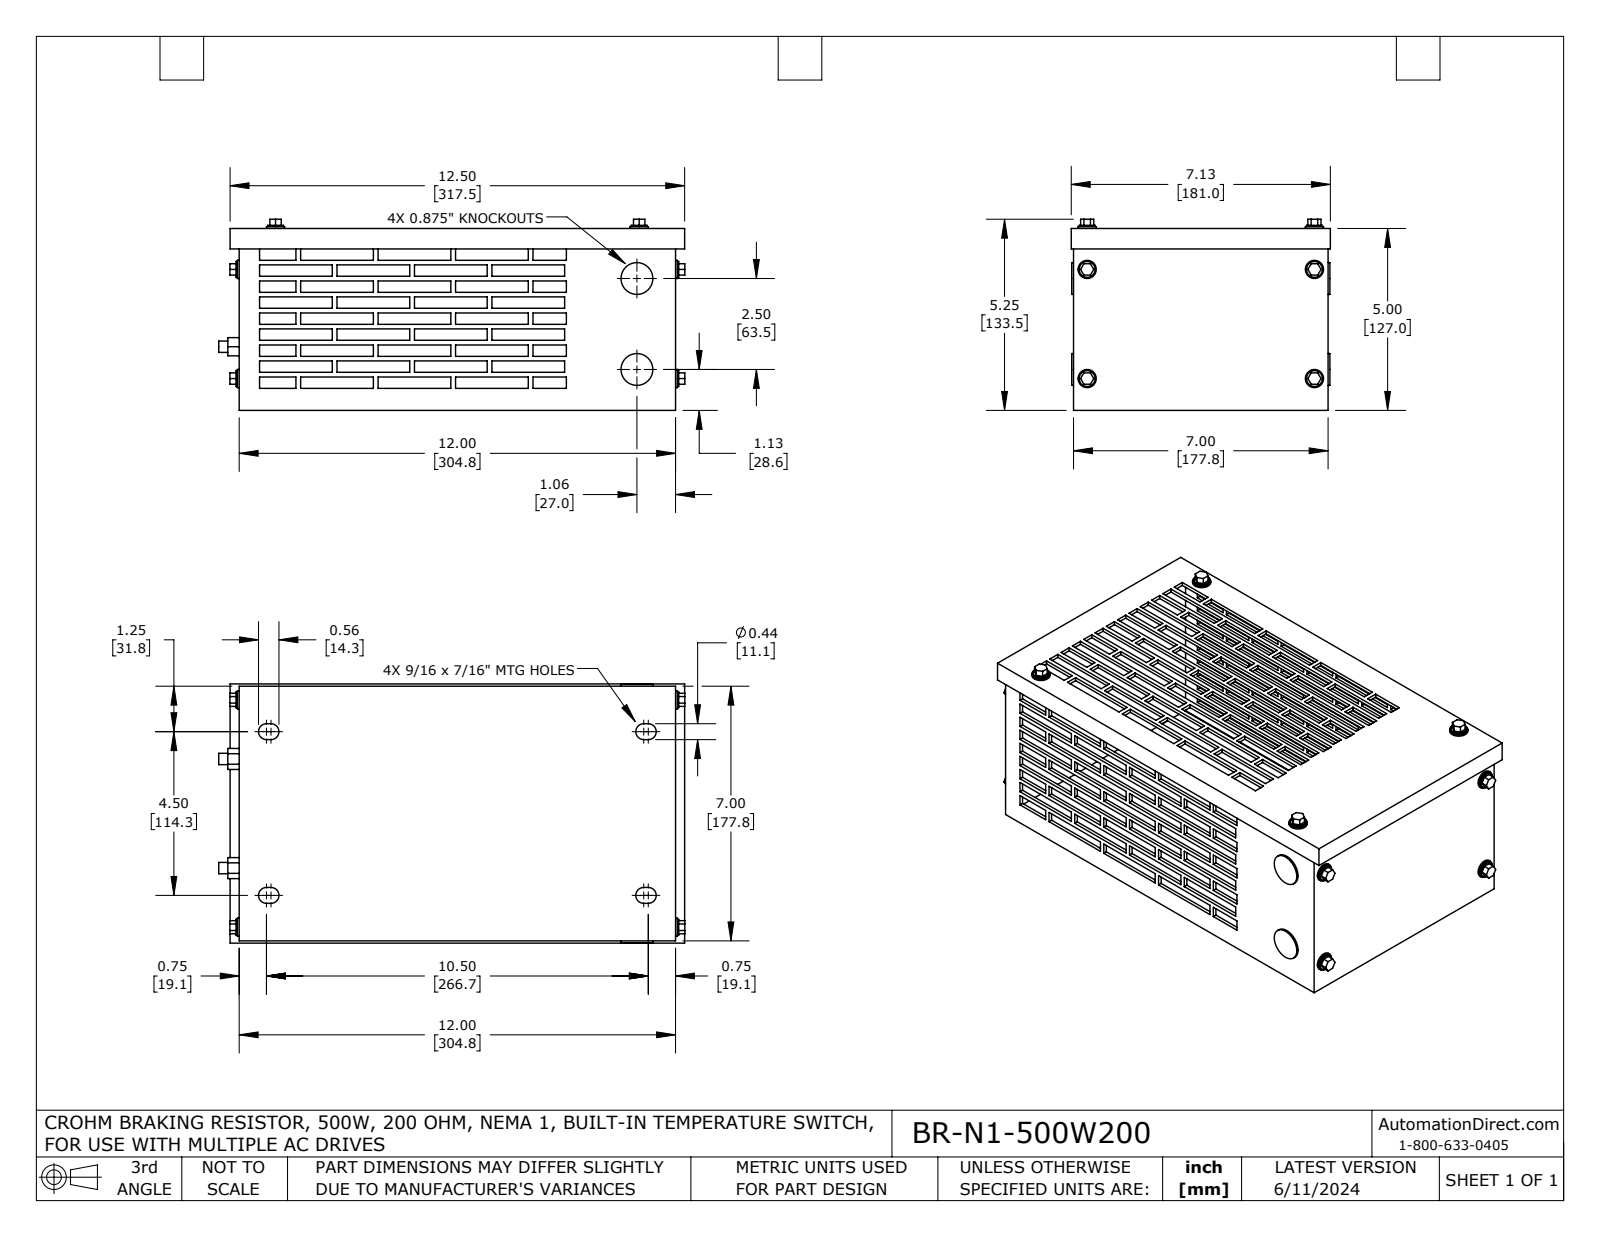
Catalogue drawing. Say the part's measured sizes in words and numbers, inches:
The part is named "BR-N1-500W200". Its 3-D file was written by "SolidWorks 2021 (AUTOMOTIVE_DESIGN)". It is 31 solids with 846 faces: 746 planar, 100 cylindrical and 0 other. Overall it measures 12.817 by 7.125 by 5.254 inches. Its volume is 28.59 cubic inches and its surface area 639.2 square inches. Round holes: 8 of diameter 0.25, 2 of diameter 0.75. Round bosses or shafts: 8 of diameter 0.5, 8 of diameter 0.437, 2 of diameter 0.875, 2 of diameter 0.313. Partial cylindrical surfaces (rounded edges, fillets, slot ends): 8 of radius 0.219. The main face-to-face distances are 0.1, 4.9, 11.9, 6.9, 5, 4.8, 12, 7, 11.8, 6.8. The hole center spacings are 6.25, 3, 6.933, 10, 11.793, 2.5.
